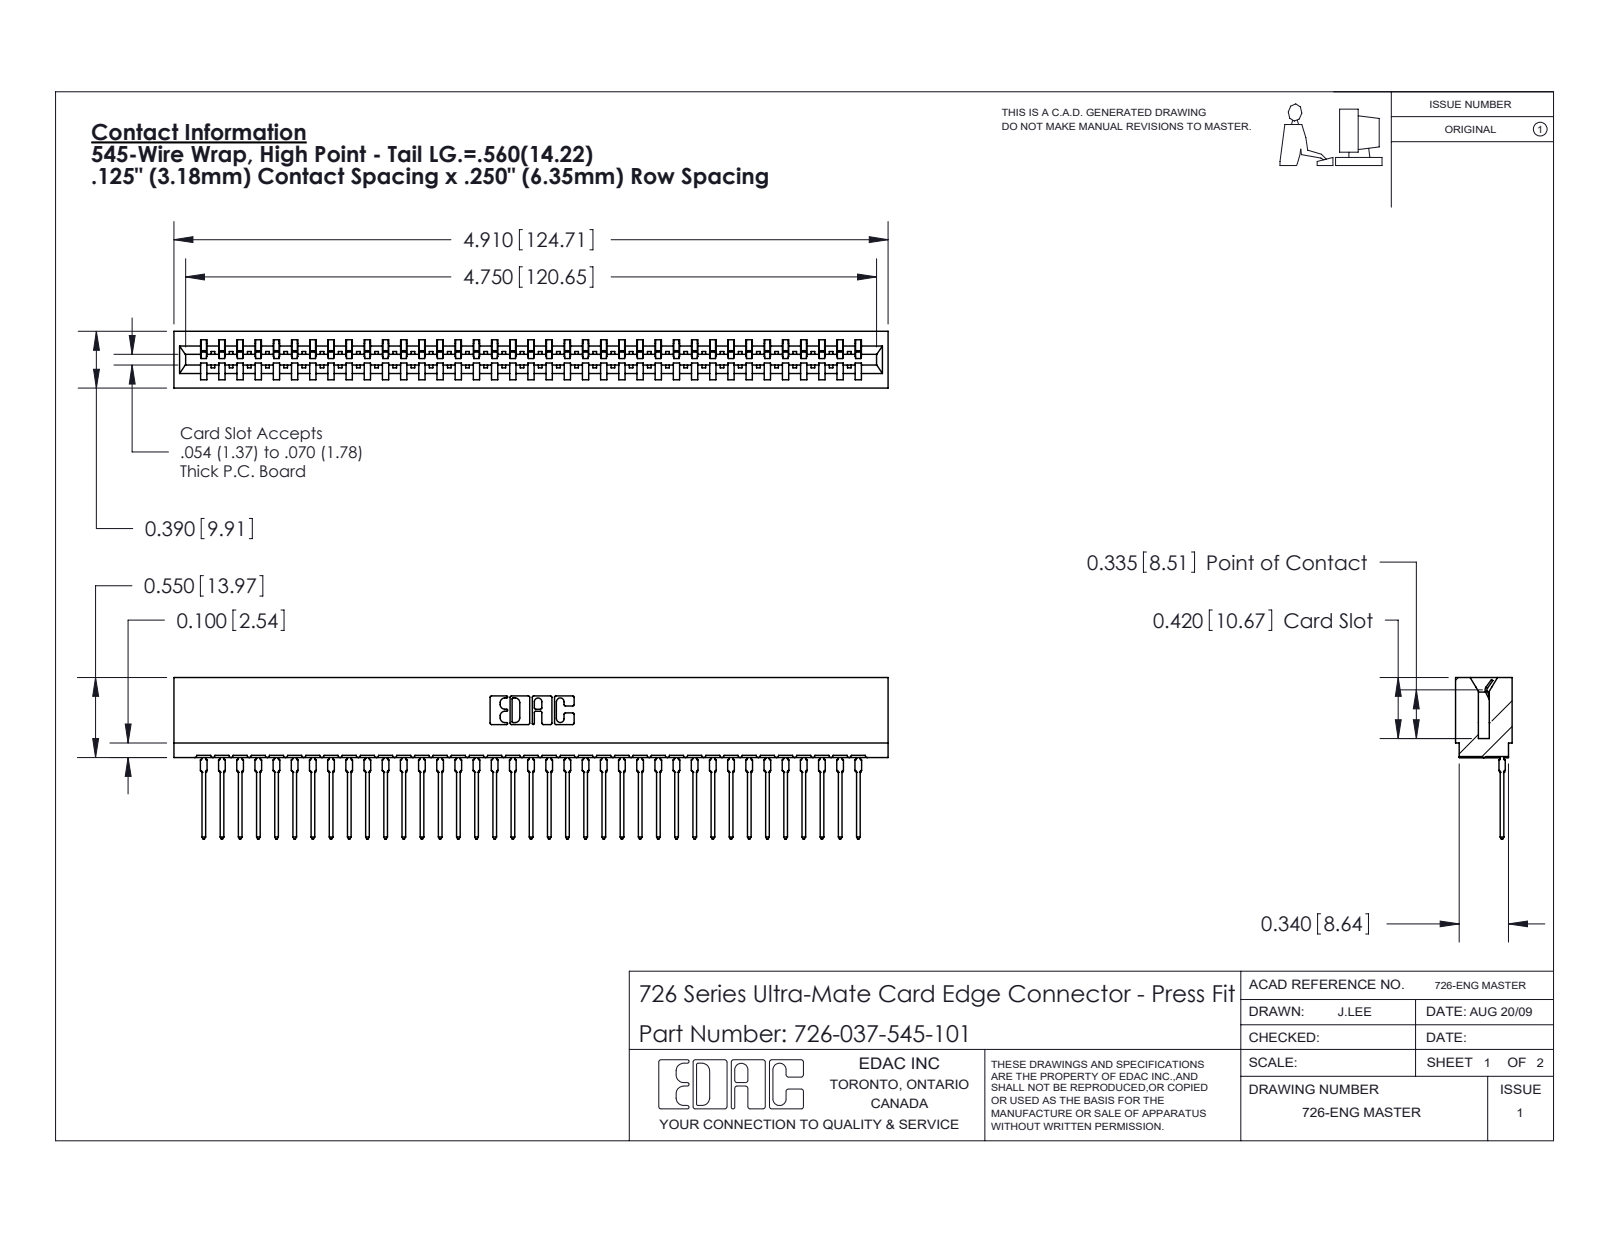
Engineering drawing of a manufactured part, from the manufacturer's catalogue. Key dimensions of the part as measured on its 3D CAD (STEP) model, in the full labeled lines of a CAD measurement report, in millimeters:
Part name (STEP PRODUCT): 726-037-545-101; 726 Part_.515 Slot Depth - 01; 746-292-001_545
STEP written by: SolidWorks 2020 (CONFIG_CONTROL_DESIGN)
Units: millimetres
Bodies: 38 solids, 4093 faces (2386 planar, 745 cylindrical, 962 other)
Overall size (bounding box): 124.7 × 28.2 × 9.9
Volume: 11 300 mm³ · Surface area: 17 640 mm²
Partial cylindrical surfaces — rounded edges, fillets, slot ends (radius × count): R0.5 ×74, R0.4 ×38, R0.3 ×22, R0.2 ×6, R0.8 ×6, R0.1 ×4, R0.3 ×4, R0.7 ×3
Main face-to-face distances: 1.4, 8.5, 9.9, 6.4, 0.6, 7.8, 2.1, 12.7, 7, 9.3
